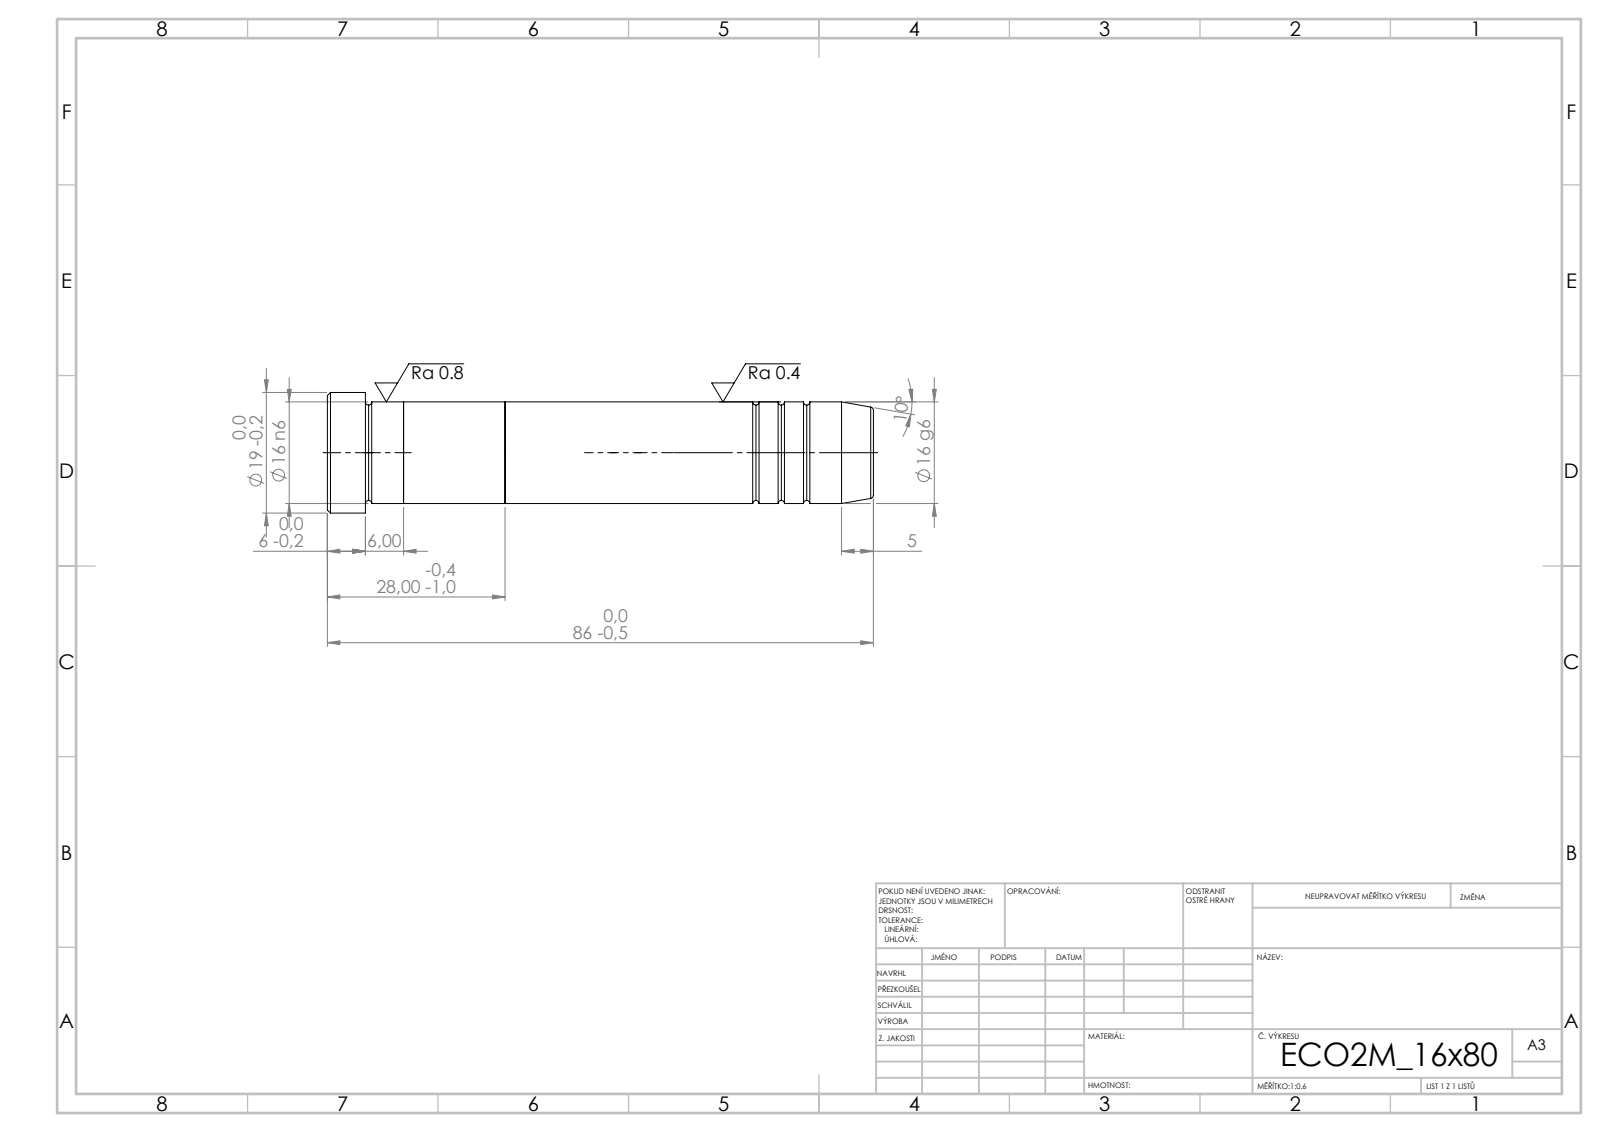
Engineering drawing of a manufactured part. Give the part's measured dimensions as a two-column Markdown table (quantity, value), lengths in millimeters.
| quantity | value |
| --- | --- |
| STEP written by | SolidWorks 2019 (CONFIG_CONTROL_DESIGN) |
| units | millimeters |
| bodies | 3 solids, 43 faces (7 planar, 14 cylindrical, 22 other) |
| overall size | 86 × 19 × 19 |
| volume | 17 594 mm³ |
| surface area | 5 777 mm² |
| round bosses / shafts (diameter × count) | 19 × 1, 16 × 1 |
| main face-to-face distances | 16, 28, 12, 6, 58, 74, 86, 80, 22 |
